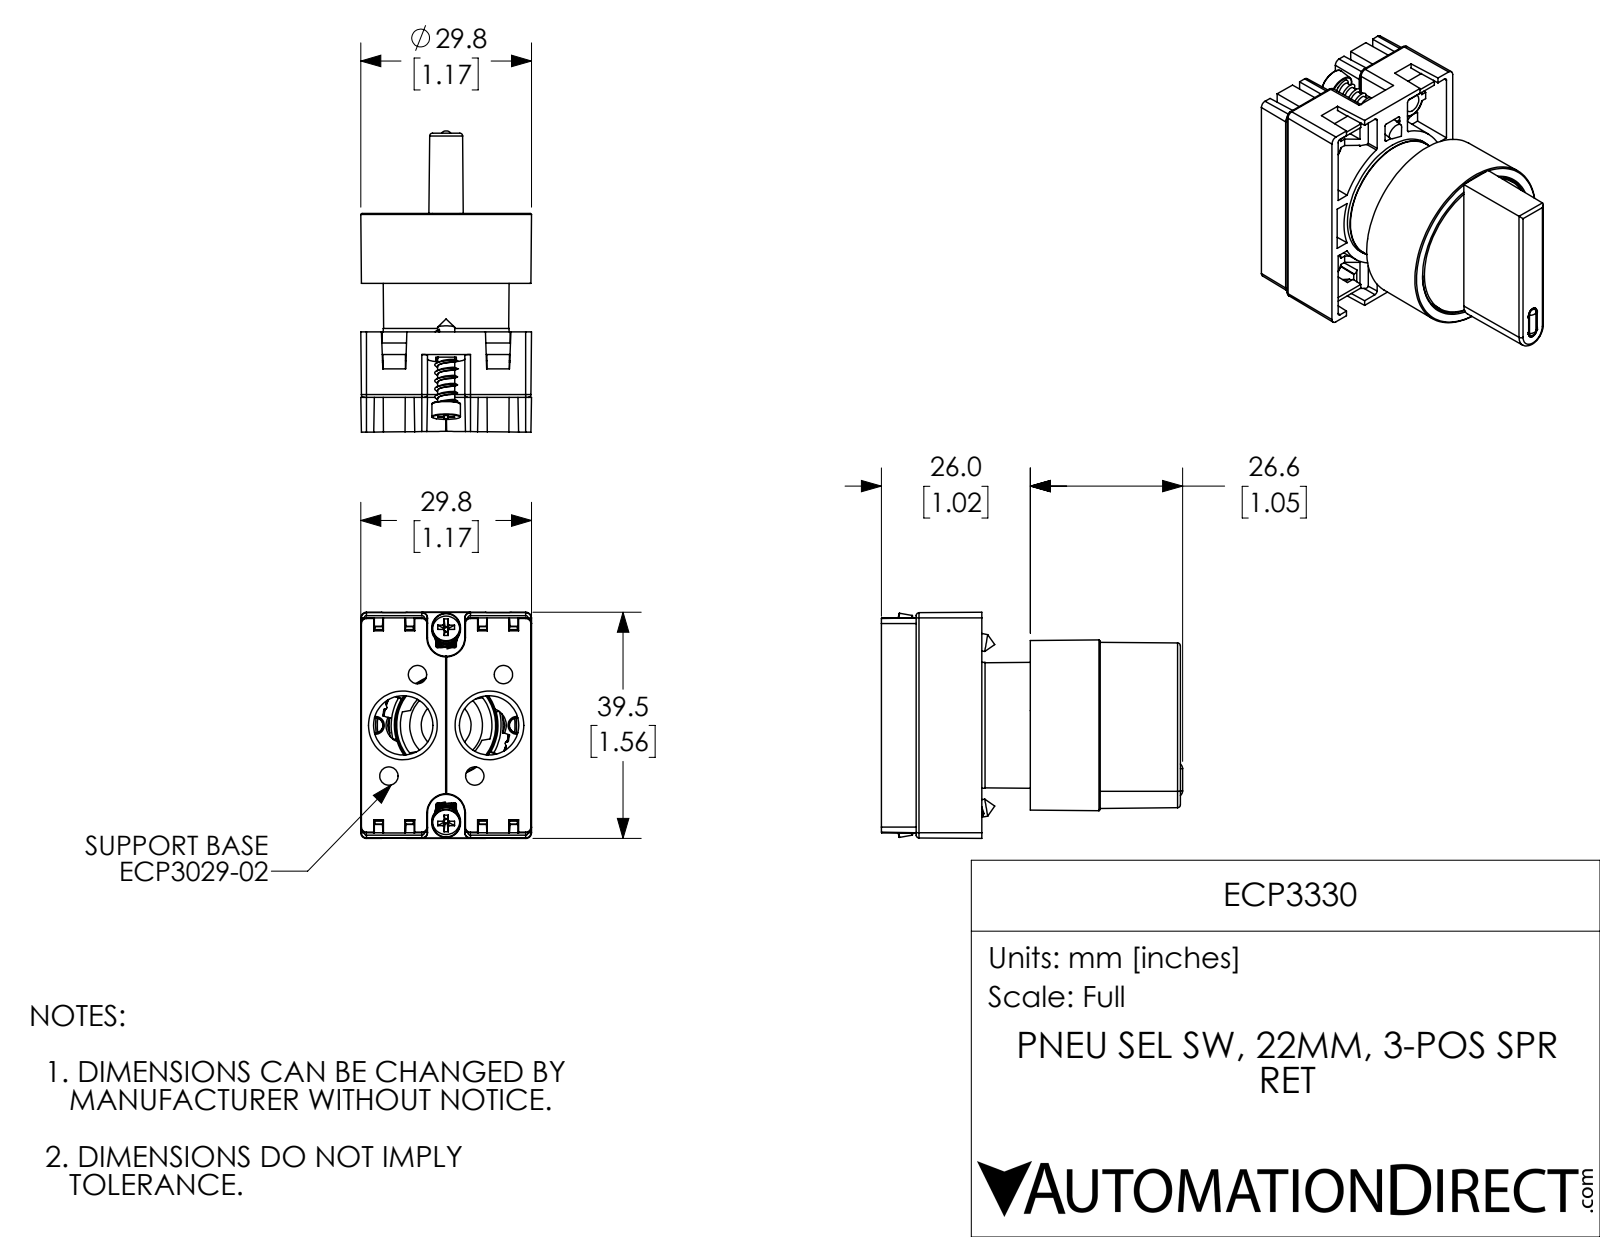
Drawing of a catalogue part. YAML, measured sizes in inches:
part_name: "ECP3330"
step_written_by: "SolidWorks 2017 (AUTOMOTIVE_DESIGN)"
units: inches
bodies: {solids: 8, faces: 839, planar: 404, cylindrical: 157, other: 278}
overall_size: [2.071, 1.555, 1.173]
volume: 1.095
surface_area: 31.53
round_holes:
  - {diameter: 0.081, count: 4}
  - {diameter: 0.407, count: 2}
  - {diameter: 0.5, count: 1}
  - {diameter: 0.551, count: 1}
  - {diameter: 0.697, count: 1}
  - {diameter: 0.75, count: 1}
  - {diameter: 0.756, count: 1}
  - {diameter: 0.854, count: 1}
  - {diameter: 0.976, count: 1}
  - {diameter: 1.024, count: 1}
round_bosses_or_shafts:
  - {diameter: 0.197, count: 2}
  - {diameter: 0.118, count: 2}
  - {diameter: 1.004, count: 1}
  - {diameter: 0.866, count: 1}
  - {diameter: 0.85, count: 1}
  - {diameter: 0.669, count: 1}
  - {diameter: 0.343, count: 1}
partial_cylinders:
  - {radius: 0.02, count: 21}
  - {radius: 0.012, count: 10}
  - {radius: 0.039, count: 9}
  - {radius: 0.006, count: 8}
  - {radius: 0.008, count: 4}
  - {radius: 0.008, count: 2}
  - {radius: 0.118, count: 2}
  - {radius: 0.128, count: 2}
face_to_face_distances: [1.265, 0.059, 0.067, 0.712, 0.743, 0.299, 0.712, 0.715, 0.814, 0.451]
hole_center_spacings: [0.304, 0.541, 0.817, 0.295, 0.472, 0.972, 1.081, 0.591]
